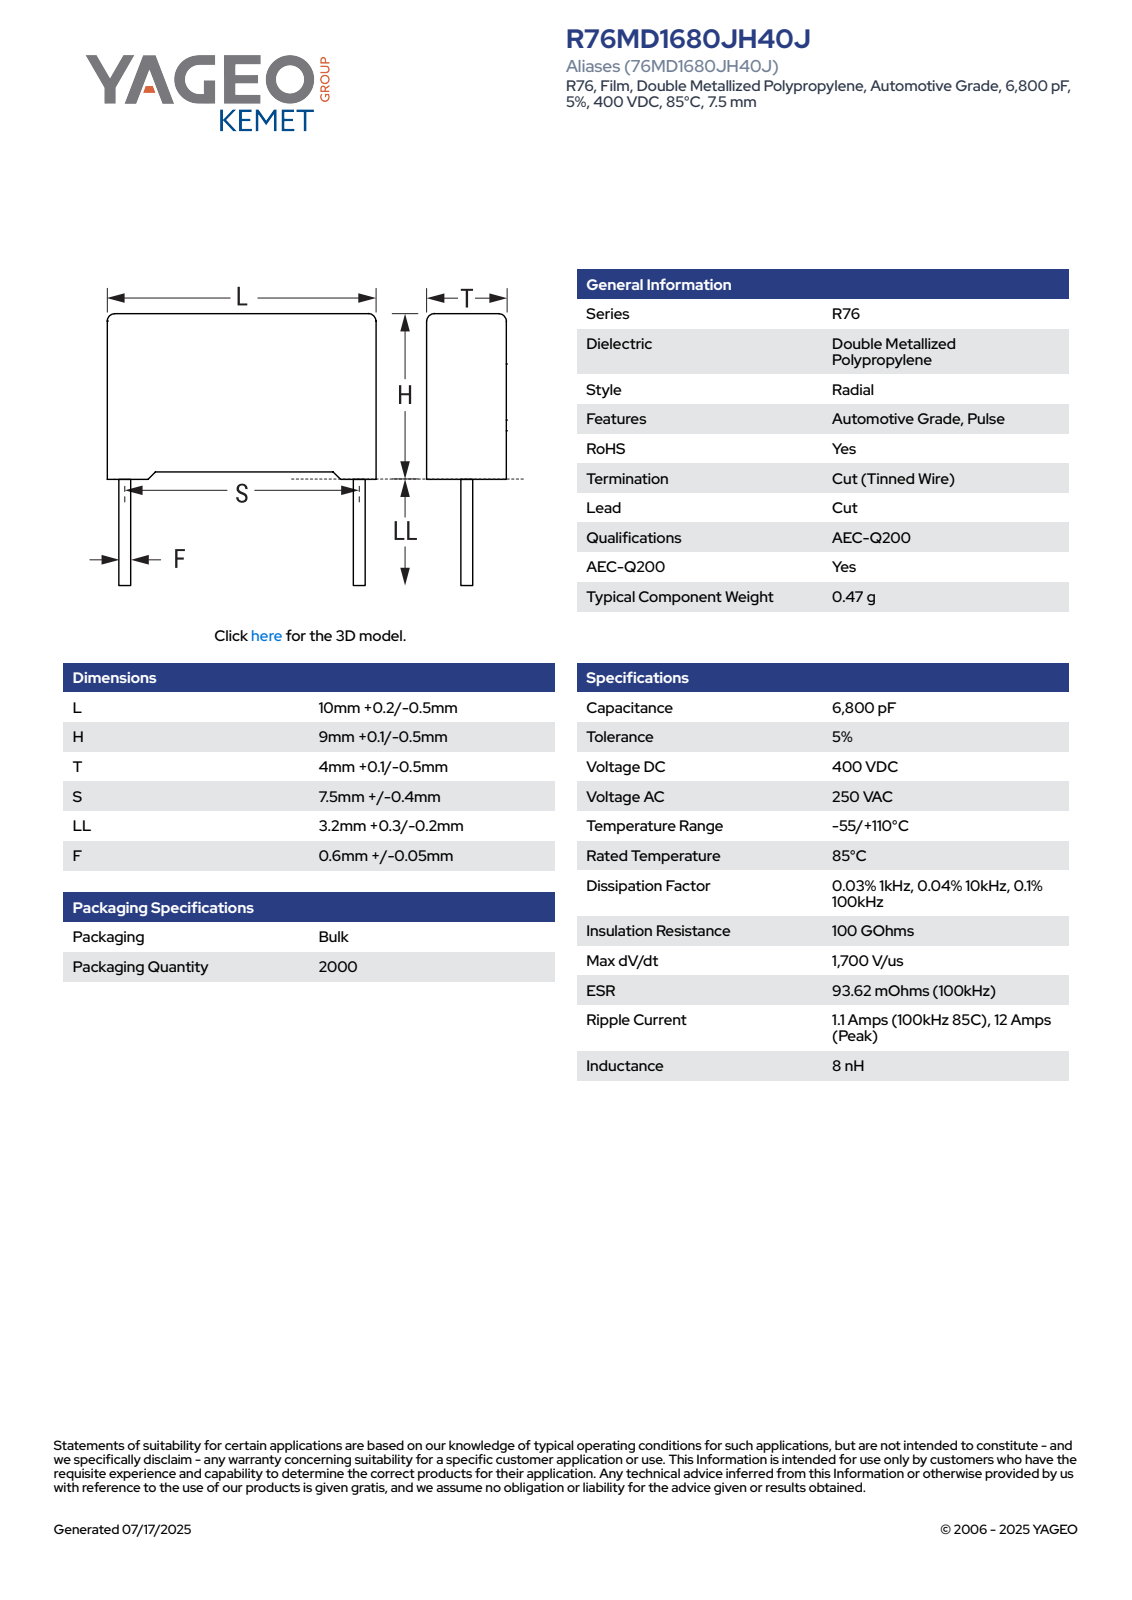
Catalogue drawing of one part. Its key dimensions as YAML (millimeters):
part_name: "CFR_RB2_10X9X4_L10.2H9.1T4.1S7.5LL3.5F0.65"
step_written_by: "SolidWorks 2021 (AUTOMOTIVE_DESIGN)"
units: millimeters
bodies: {solids: 4, faces: 85, planar: 77, cylindrical: 8, other: 0}
overall_size: [12.6, 10.2, 4.11]
volume: 357
surface_area: 377
round_bosses_or_shafts:
  - {diameter: 0.65, count: 2}
partial_cylinders:
  - {radius: 0.5, count: 4}
face_to_face_distances: [4.1, 10.2, 8.35, 0.34, 3.76, 0.75, 9.1, 3.42, 9.86, 0.31]
